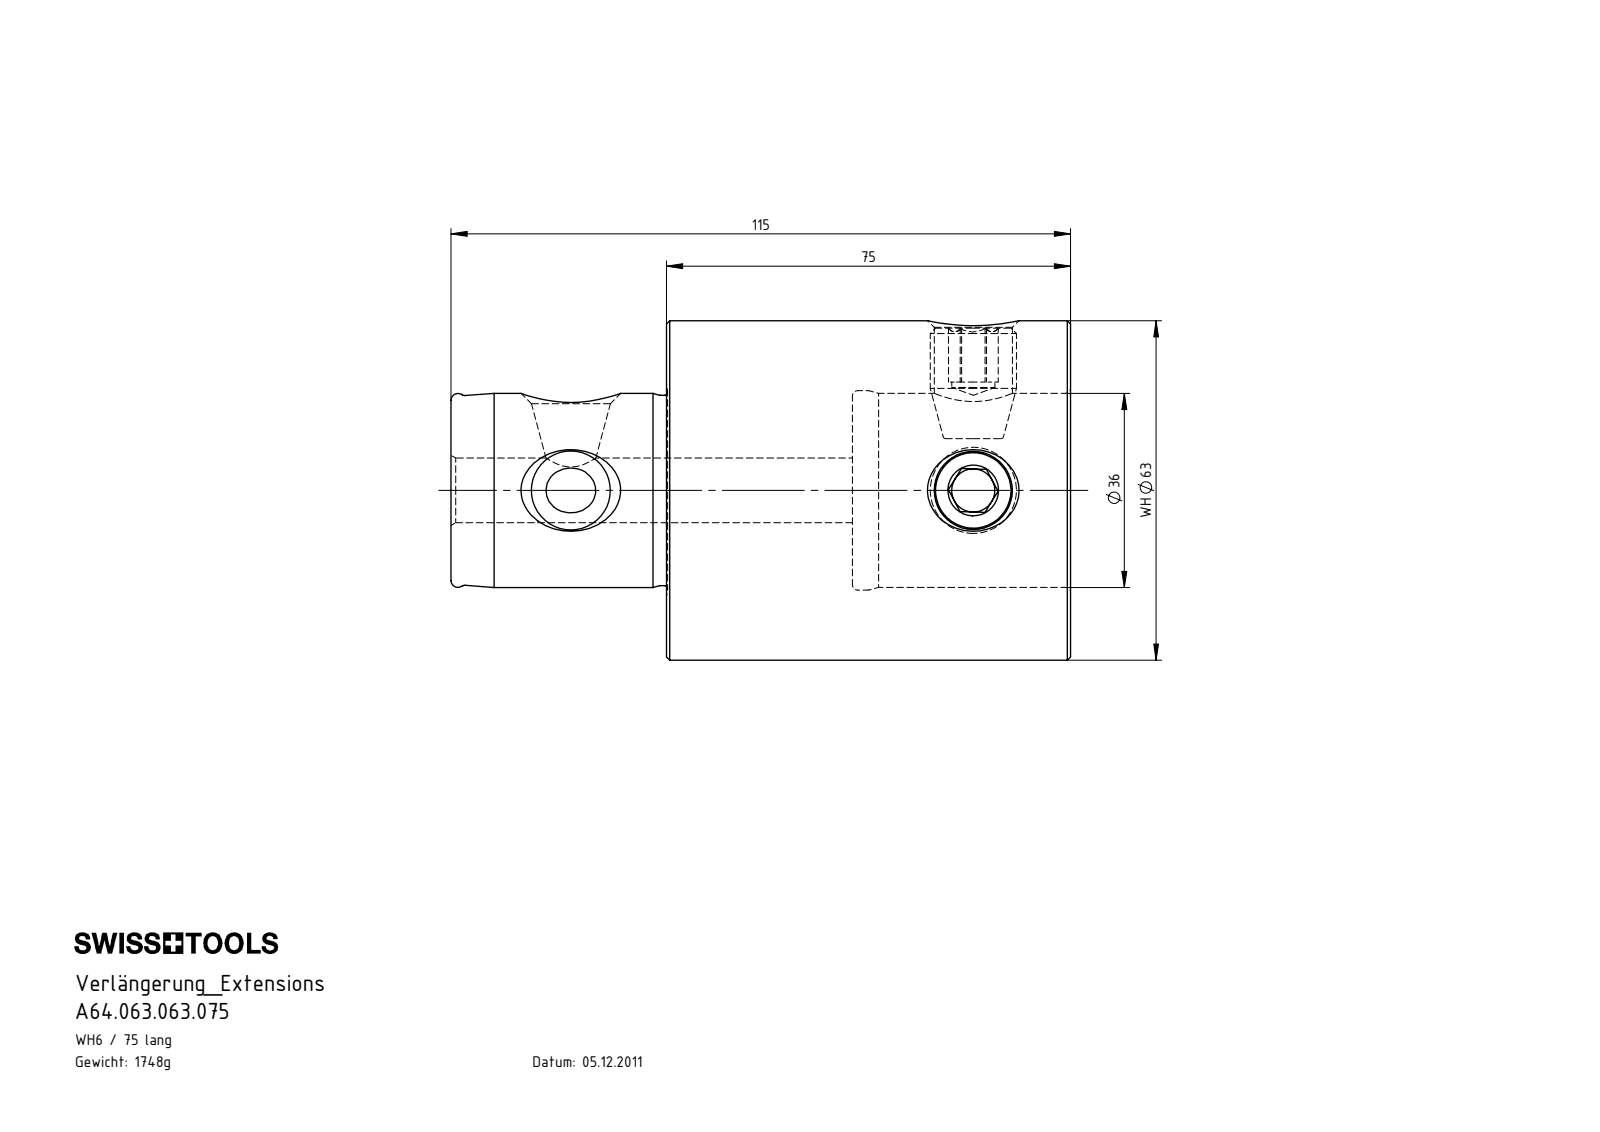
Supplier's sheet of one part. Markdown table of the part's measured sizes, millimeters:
| quantity | value |
| --- | --- |
| part name | WH6-WH6.001.075; WH6-ER1.001.021; WH6-WH6.001.075_A |
| STEP written by | SolidWorks 2012 (CONFIG_CONTROL_DESIGN) |
| units | millimeters |
| bodies | 3 solids, 94 faces (22 planar, 20 cylindrical, 52 other) |
| overall size | 115 × 63 × 63 |
| volume | 222 568 mm³ |
| surface area | 36 694 mm² |
| round holes (diameter × count) | 14.5 × 2, 12 × 1, 36 × 1, 37 × 1 |
| round bosses / shafts (diameter × count) | 16 × 2, 63 × 1, 35.3 × 1 |
| main face-to-face distances | 75, 34.5, 40.5, 40, 74.5, 115, 8, 20.5, 8.5, 12 |
